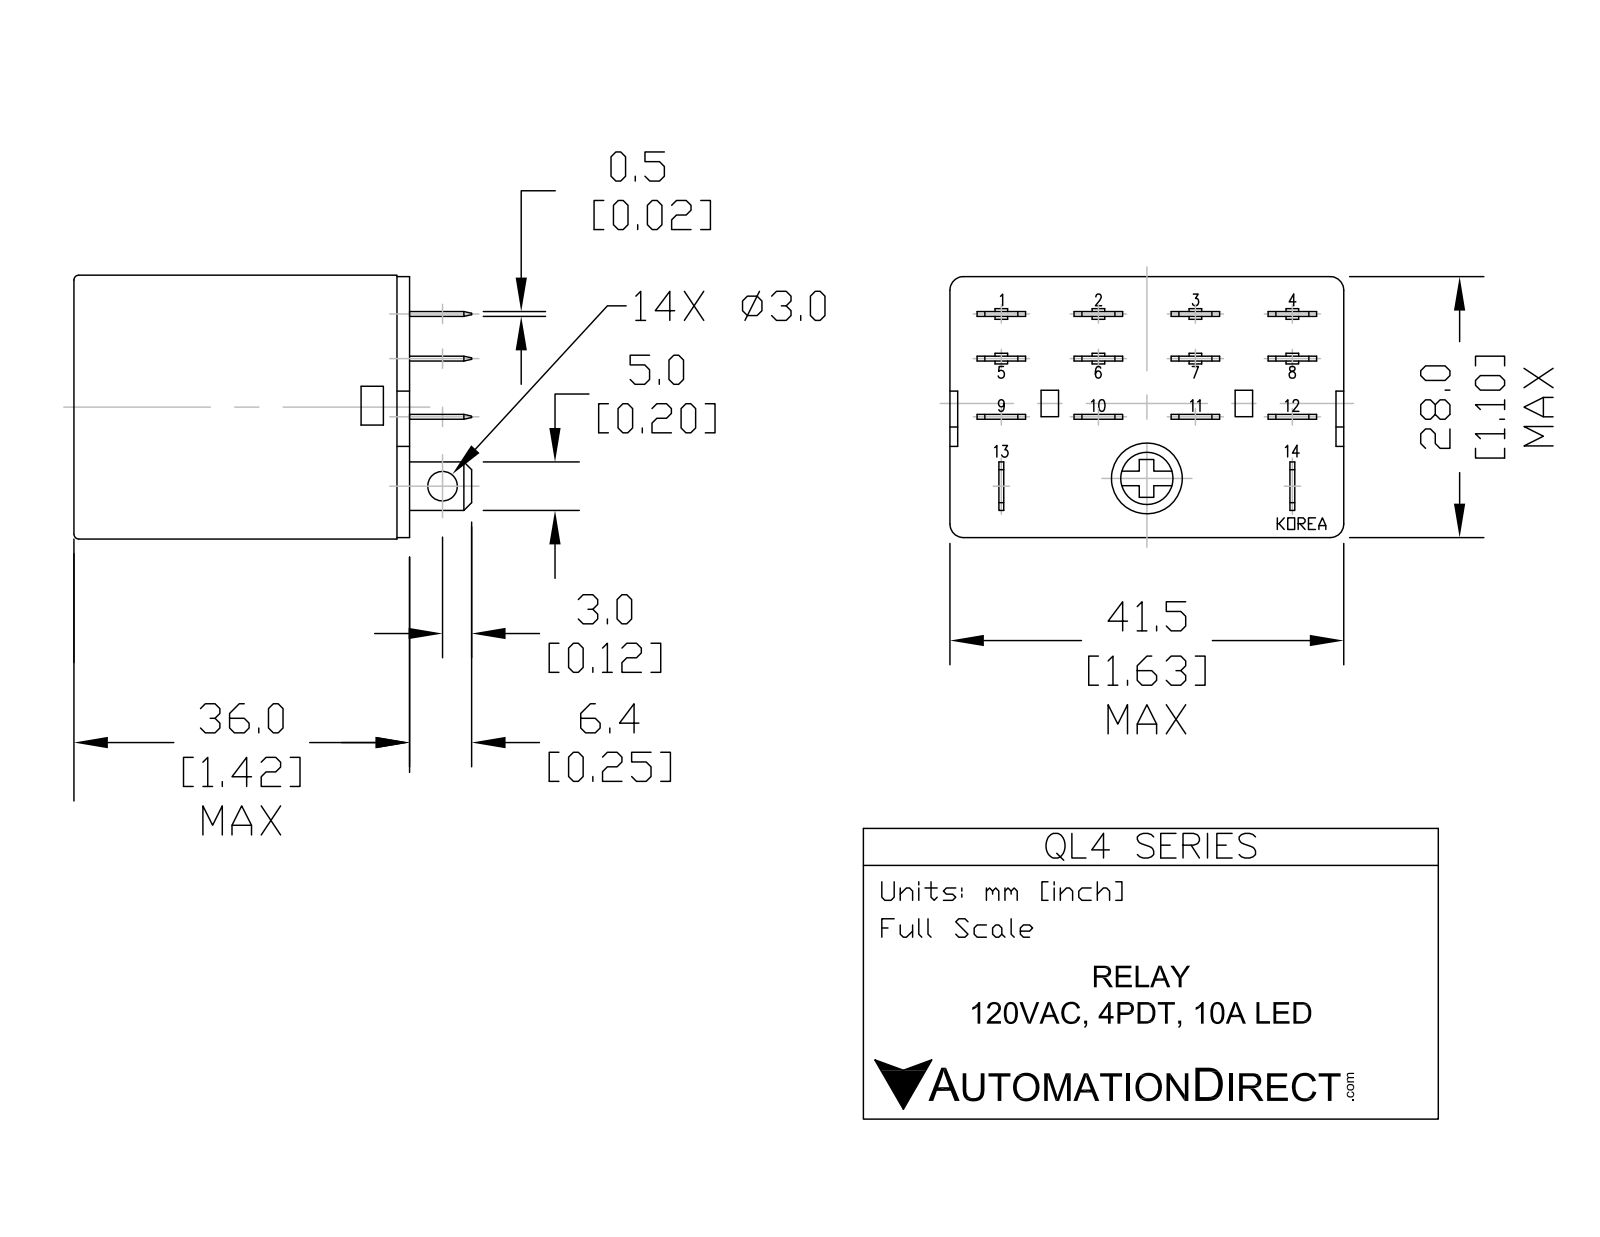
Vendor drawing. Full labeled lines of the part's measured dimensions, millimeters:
Part name (STEP PRODUCT): QL4N1-A120
STEP written by: SolidWorks 2013 (AUTOMOTIVE_DESIGN)
Units: millimetres
Bodies: 1 solid, 191 faces (143 planar, 44 cylindrical, 4 other)
Overall size (bounding box): 42.4 × 41.5 × 28
Volume: 41 145 mm³ · Surface area: 7 956 mm²
Round holes (diameter × count): ⌀3 ×5, ⌀6.5 ×1
Round bosses / shafts (diameter × count): ⌀4 ×1
Partial cylindrical surfaces — rounded edges, fillets, slot ends (radius × count): R1 ×8
Main face-to-face distances: 36, 4.5, 0.5, 5, 4, 9, 8.5, 9.5, 30, 2.5
Hole centre spacings: 9.87, 9.88, 10.75, 20.62, 20.63, 30.5
